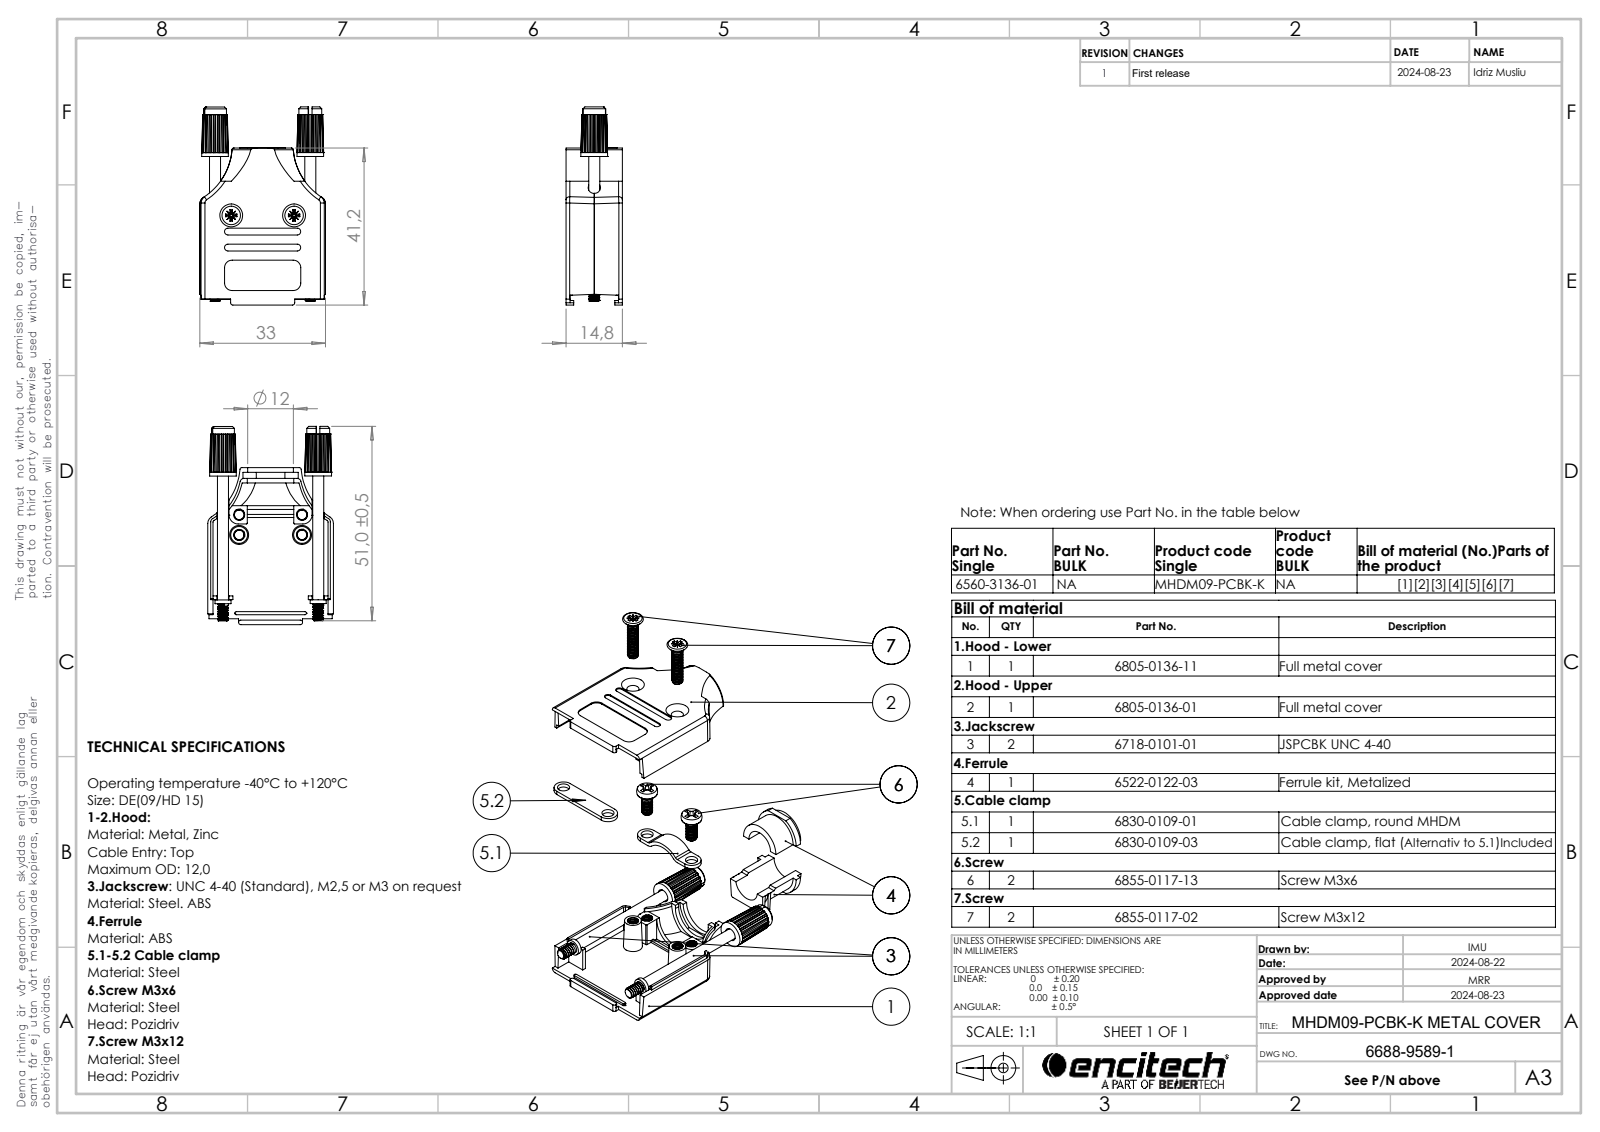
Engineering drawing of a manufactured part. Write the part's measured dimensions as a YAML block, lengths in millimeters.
part_name: "6805-0136-01; 6522-0122-03 (8mm LV); 6830-0109-01; 6522-0122-03 (8mm SV) (+5 more)"
step_written_by: "SolidWorks 2021 (AUTOMOTIVE_DESIGN)"
units: millimeters
bodies: {solids: 11, faces: 836, planar: 407, cylindrical: 329, other: 100}
overall_size: [47.53, 33, 14.8]
volume: 6301
surface_area: 11864
round_holes:
  - {diameter: 3.2, count: 6}
  - {diameter: 3, count: 4}
  - {diameter: 4.55, count: 2}
  - {diameter: 8, count: 1}
  - {diameter: 12.2, count: 1}
round_bosses_or_shafts:
  - {diameter: 2.9, count: 4}
  - {diameter: 5.2, count: 2}
  - {diameter: 4, count: 2}
  - {diameter: 3, count: 2}
  - {diameter: 2.8, count: 2}
  - {diameter: 12, count: 1}
partial_cylinders:
  - {radius: 0.1, count: 12}
  - {radius: 1, count: 12}
  - {radius: 16.42, count: 10}
  - {radius: 0.25, count: 5}
  - {radius: 0.5, count: 4}
  - {radius: 0.9, count: 4}
  - {radius: 2, count: 4}
  - {radius: 0.4, count: 2}
face_to_face_distances: [1.05, 13.75, 12.7, 14.8, 7.4, 6.35, 0.75, 14.5, 7.1, 13.45]
hole_center_spacings: [5.27, 12.5, 16.5, 17.32, 25]
